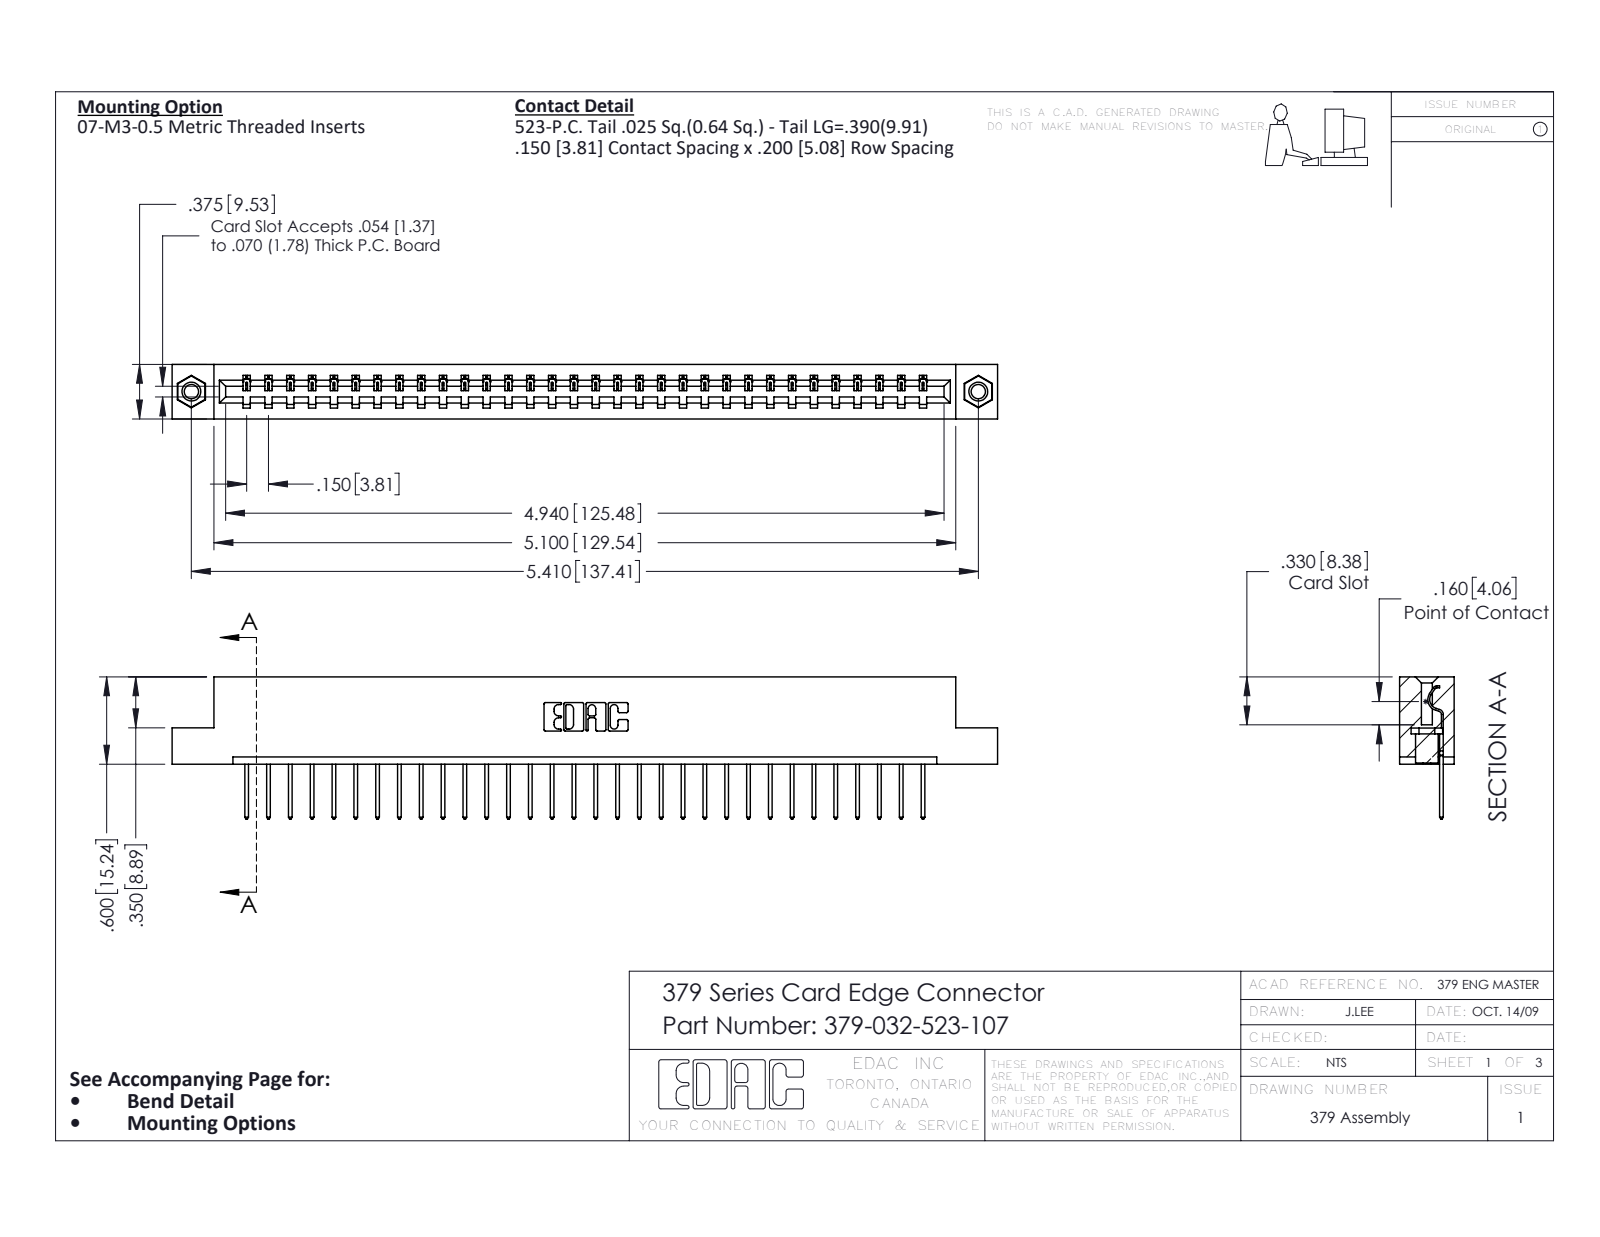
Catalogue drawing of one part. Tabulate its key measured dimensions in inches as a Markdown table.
| quantity | value |
| --- | --- |
| part name | 345-292-001_345-293-123; 345-250-001_345-250-005-103; 379-032-523-107; 379 Part_Flush - .156 Dia - TI |
| STEP written by | SolidWorks 2016 (CONFIG_CONTROL_DESIGN) |
| units | inches |
| bodies | 35 solids, 2030 faces (1446 planar, 568 cylindrical, 16 other) |
| overall size | 5.675 × 0.977 × 0.375 |
| volume | 0.915 in³ |
| surface area | 23.82 in² |
| round holes (diameter × count) | 0.098 × 2, 0.125 × 2, 0.156 × 2 |
| round bosses / shafts (diameter × count) | 0.155 × 2 |
| partial cylindrical surfaces (radius × count) | 0.006 × 64, 0.01 × 64, 0.01 × 22, 0.007 × 6, 0.031 × 6, 0.026 × 3, 0.014 × 1, 0.022 × 1 |
| main face-to-face distances | 0.3, 0.075, 0.375, 0.225, 0.2, 0.6, 0.275, 0.1, 0.025, 0.55 |
| hole center spacings | 5.41 |
